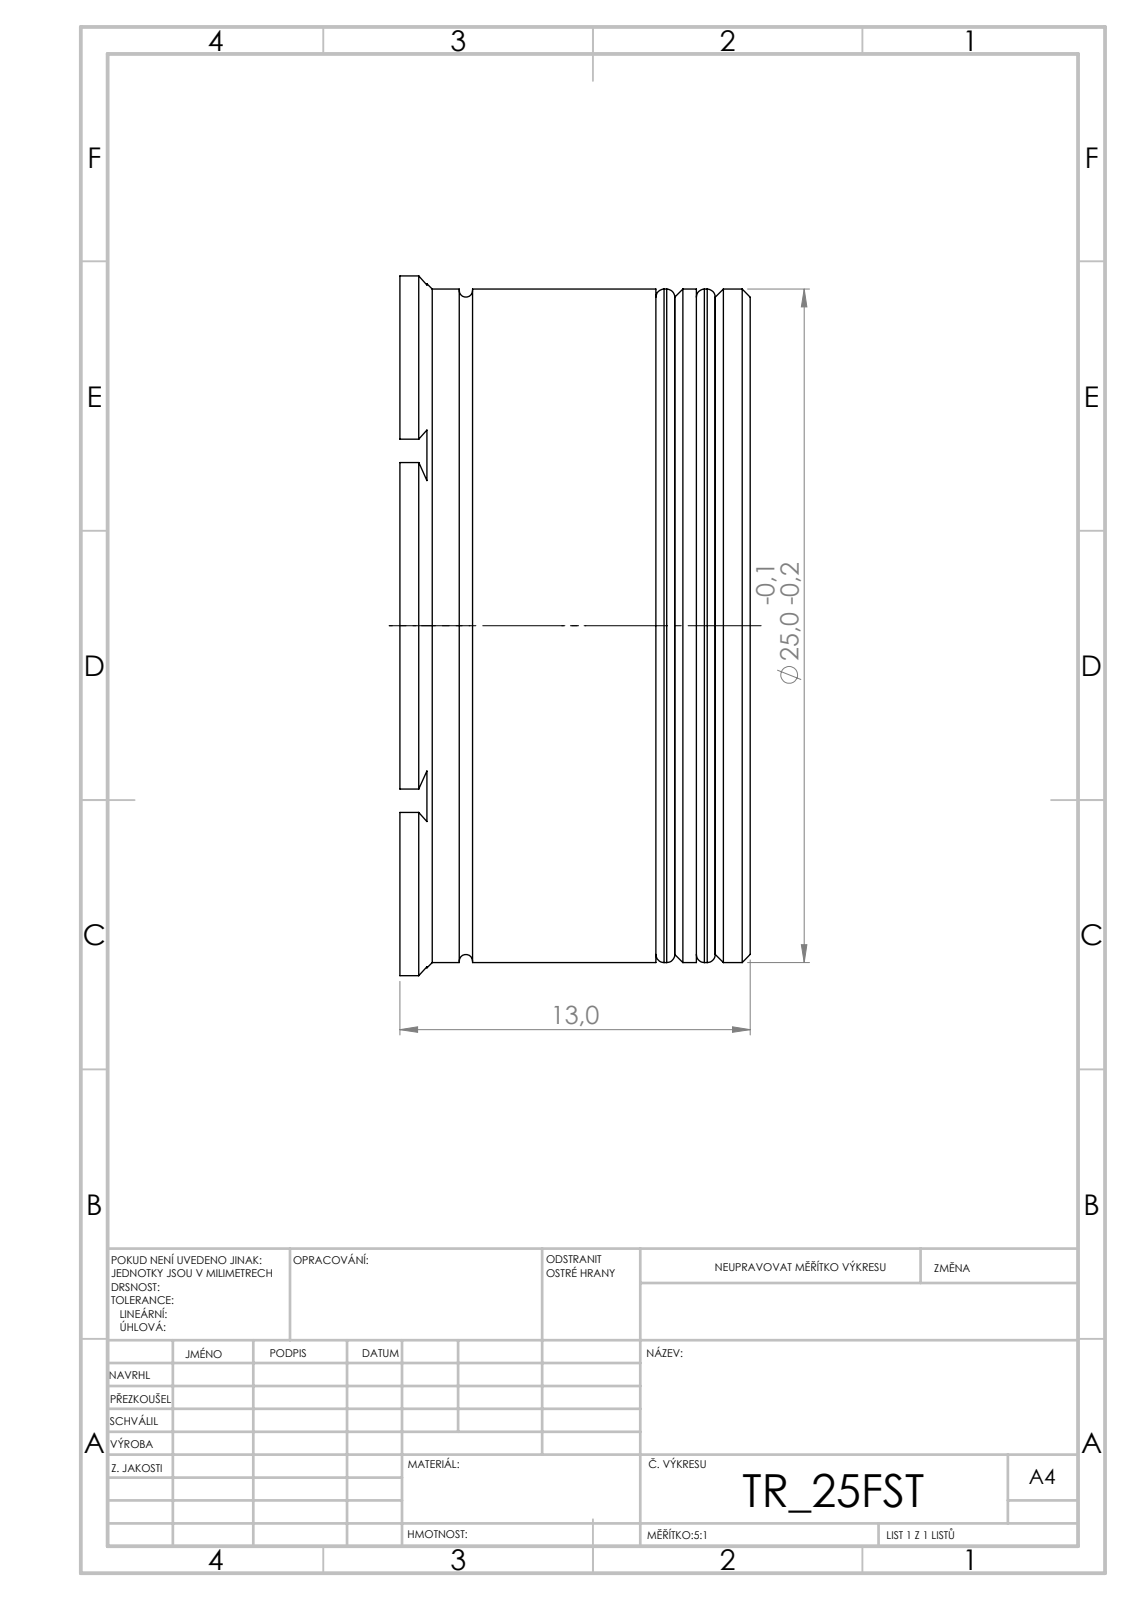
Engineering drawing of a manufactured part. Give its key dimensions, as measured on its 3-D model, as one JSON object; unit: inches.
{"step_written_by": "SolidWorks 2019 (CONFIG_CONTROL_DESIGN)", "units": "inches", "bodies": {"solids": 3, "faces": 84, "planar": 34, "cylindrical": 30, "other": 20}, "overall_size": [1.024, 1.023, 0.512], "volume_in3": 0.403, "surface_area_in2": 6.685, "round_bosses_or_shafts": [[1.024, 1], [0.984, 1], [0.961, 1]], "partial_cylinders_radius": [[0.433, 1]], "face_to_face_distances": [0.059, 0.028, 0.087, 0.079, 0.138, 0.051, 0.11, 0.031, 0.472, 0.421]}
